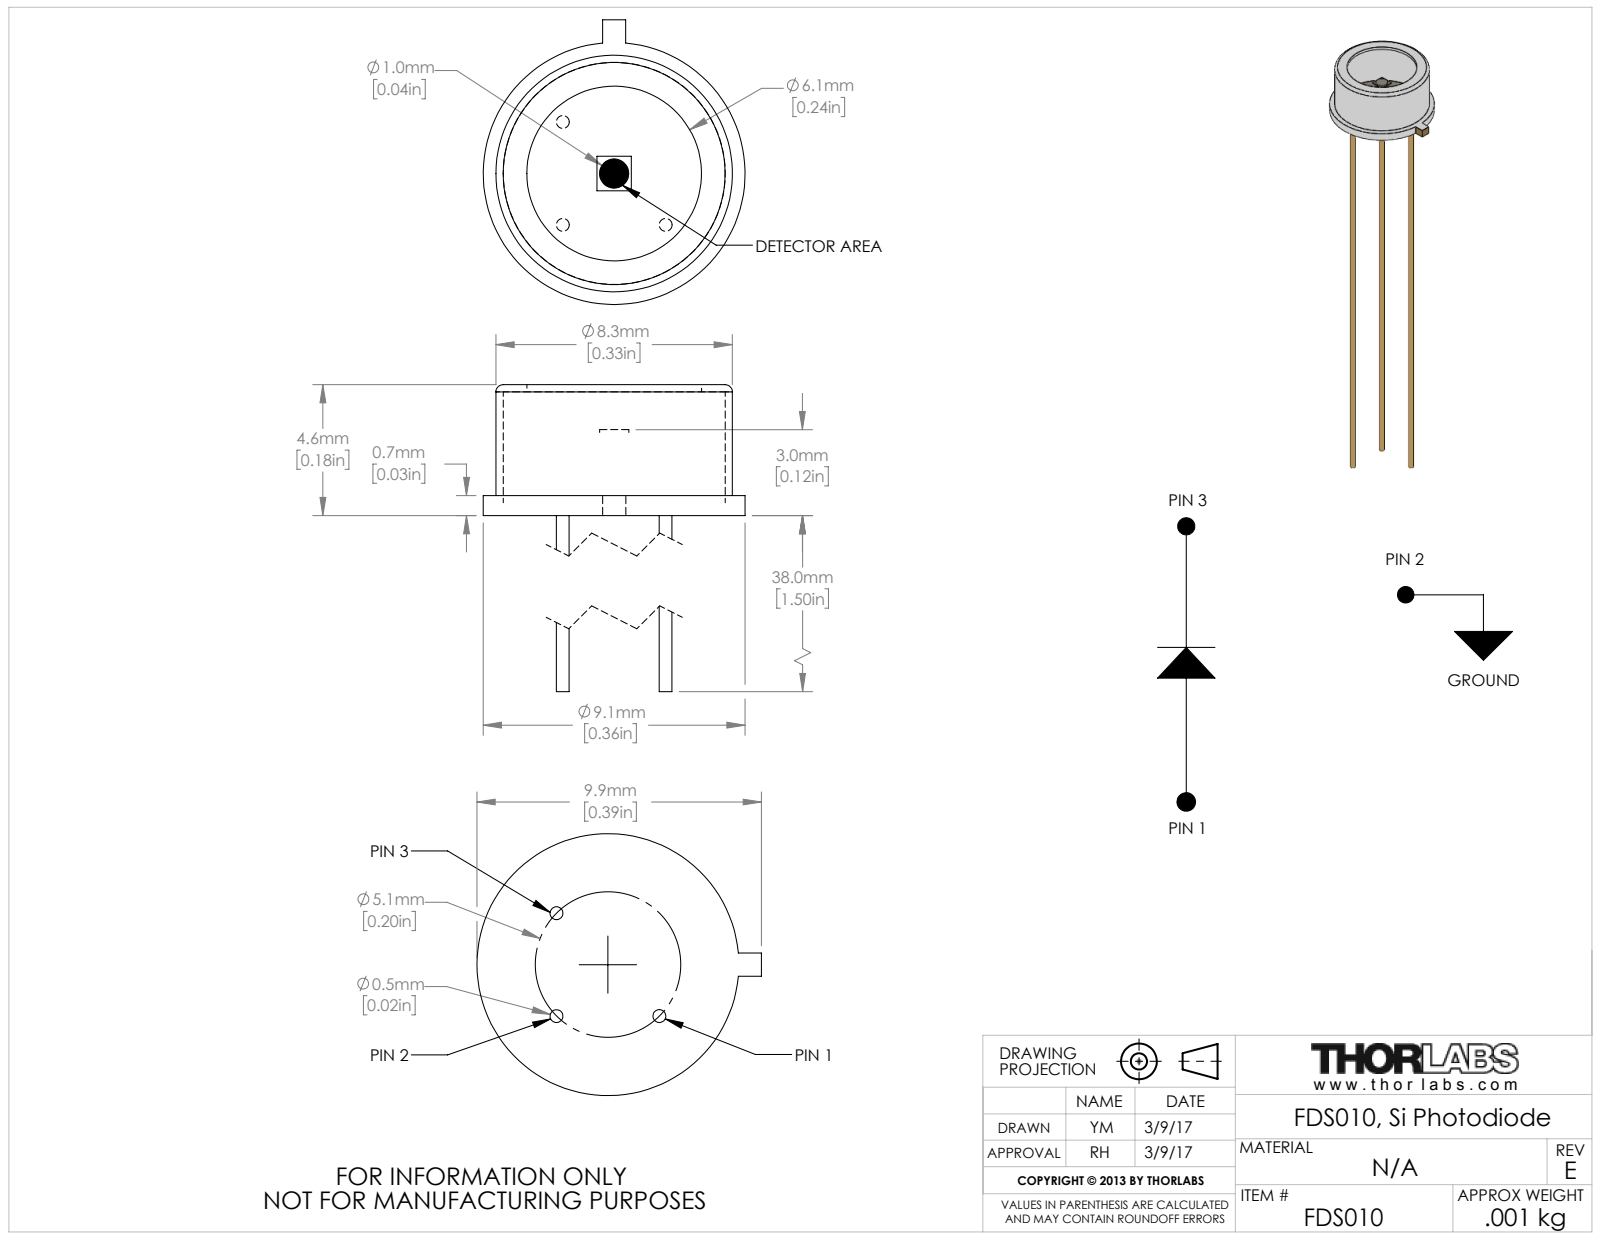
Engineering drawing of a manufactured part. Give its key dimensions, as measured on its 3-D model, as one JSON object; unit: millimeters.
{"part_name": "0636-E0W", "step_written_by": "SolidWorks 2016 (AUTOMOTIVE_DESIGN)", "units": "millimeters", "bodies": {"solids": 2, "faces": 37, "planar": 18, "cylindrical": 17, "other": 2}, "overall_size": [42.57, 9.94, 9.14], "volume_mm3": 82, "surface_area_mm2": 551, "round_holes": [[6.1, 1], [7.75, 1]], "round_bosses_or_shafts": [[0.45, 3], [9.14, 1], [8.26, 1], [1.02, 1]], "face_to_face_distances": [0.45, 3.87, 4.32, 4.57, 4.12, 0.7, 3.62, 2.85, 2.4, 2.15]}
